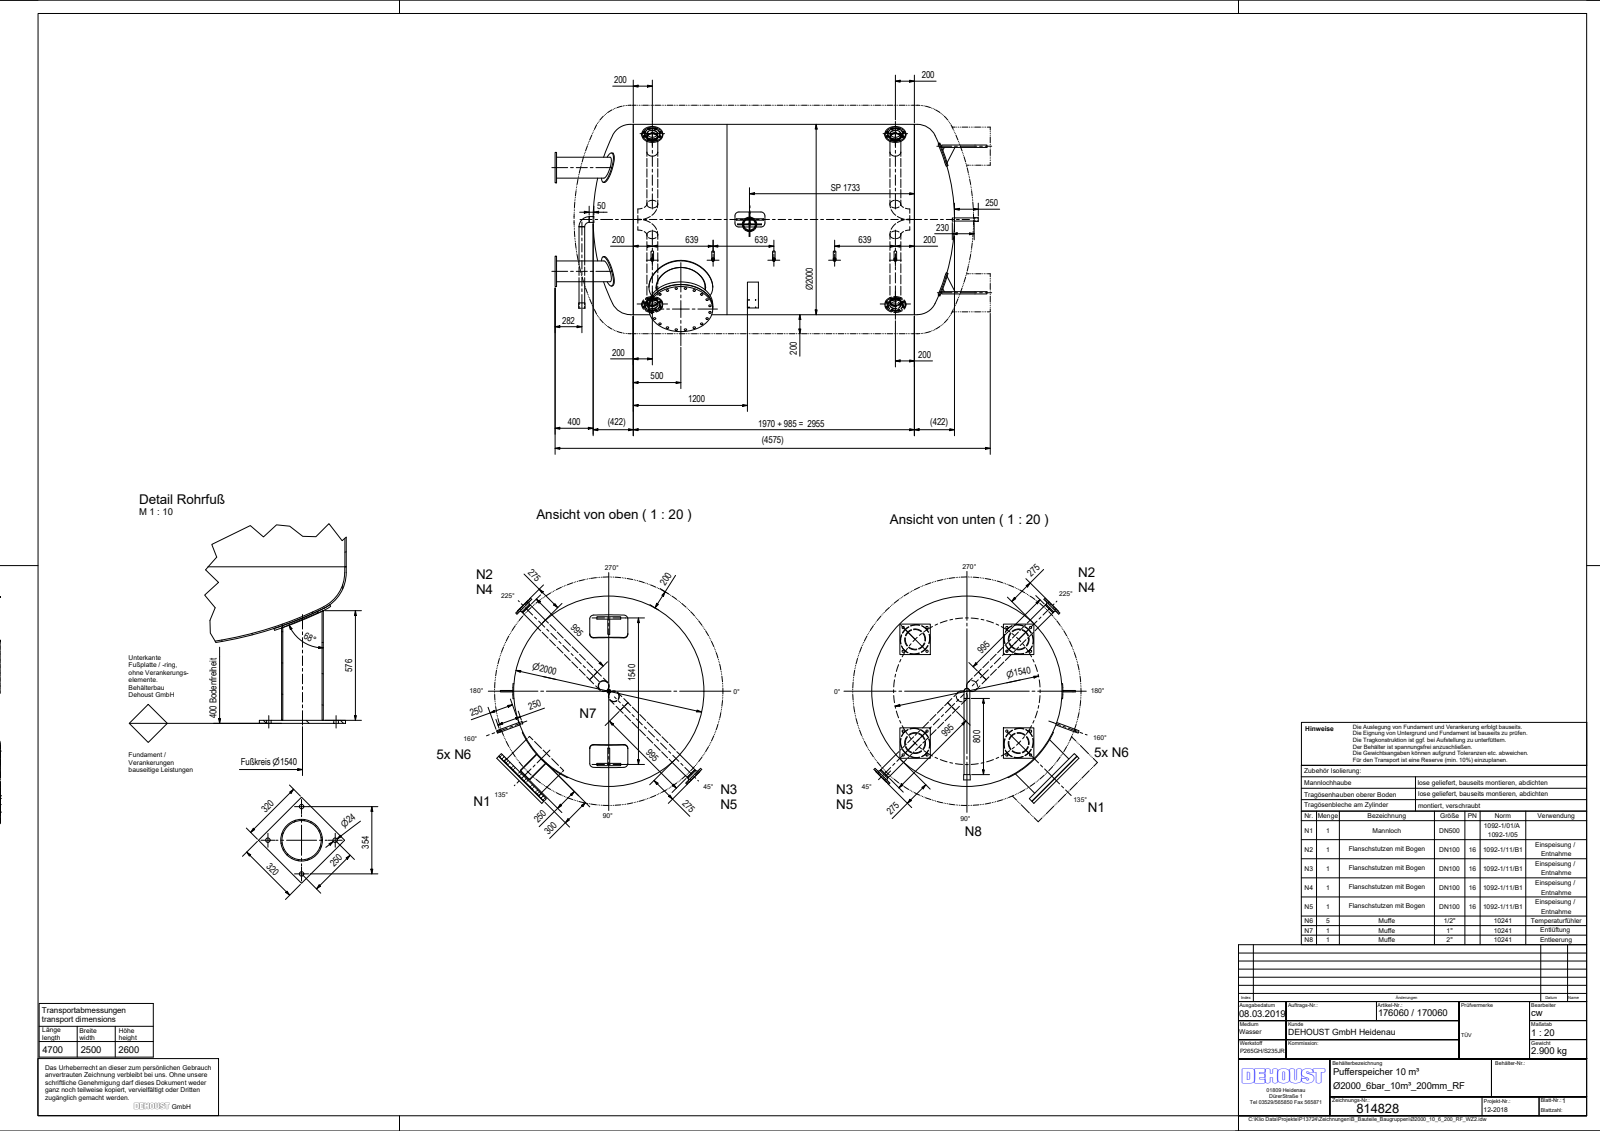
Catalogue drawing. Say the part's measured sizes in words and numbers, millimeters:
The part is named "Ø2000_10_6_200_RF_WZ2; Klöpper_Gew_Ø2000_7,8; Zyl_Ø2000_7x2955_mV_2019; TÖB_Puffer_Ø2000_7, 8_200 (+8 more)". Its 3-D file was written by "Autodesk Inventor 2019 (AUTOMOTIVE_DESIGN)". It is 57 solids with 428 faces: 166 planar, 216 cylindrical and 46 other. Overall it measures 4540.48 by 2179.13 by 2178.04 millimeters. Its volume is 315 000 000 cubic millimeters and its surface area 67 230 000 square millimeters. Round holes: 40 of diameter 26, 32 of diameter 18, 16 of diameter 24, 5 of diameter 18.63, 5 of diameter 21.7, 5 of diameter 26.9, 4 of diameter 5.8, 4 of diameter 106.3, 4 of diameter 107.1, 4 of diameter 114.3, 4 of diameter 206.5, 2 of diameter 52.3. Round bosses or shafts: 5 of diameter 26.9, 5 of diameter 26.4, 4 of diameter 320, 4 of diameter 220, 4 of diameter 219.1, 4 of diameter 158, 4 of diameter 114.3, 3 of diameter 670. Partial cylindrical surfaces (rounded edges, fillets, slot ends): 12 of radius 42, 4 of radius 10, 2 of radius 5, 2 of radius 6, 1 of radius 36, 1 of radius 72, 1 of radius 125, 1 of radius 1007. The main face-to-face distances are 400, 16, 28, 557.5, 957.5, 25, 582.5, 982.5, 1540, 1277.5. The hole center spacings are 90, 310, 2555, 638.75, 191.59, 127.28, 166.3, 552.42.
